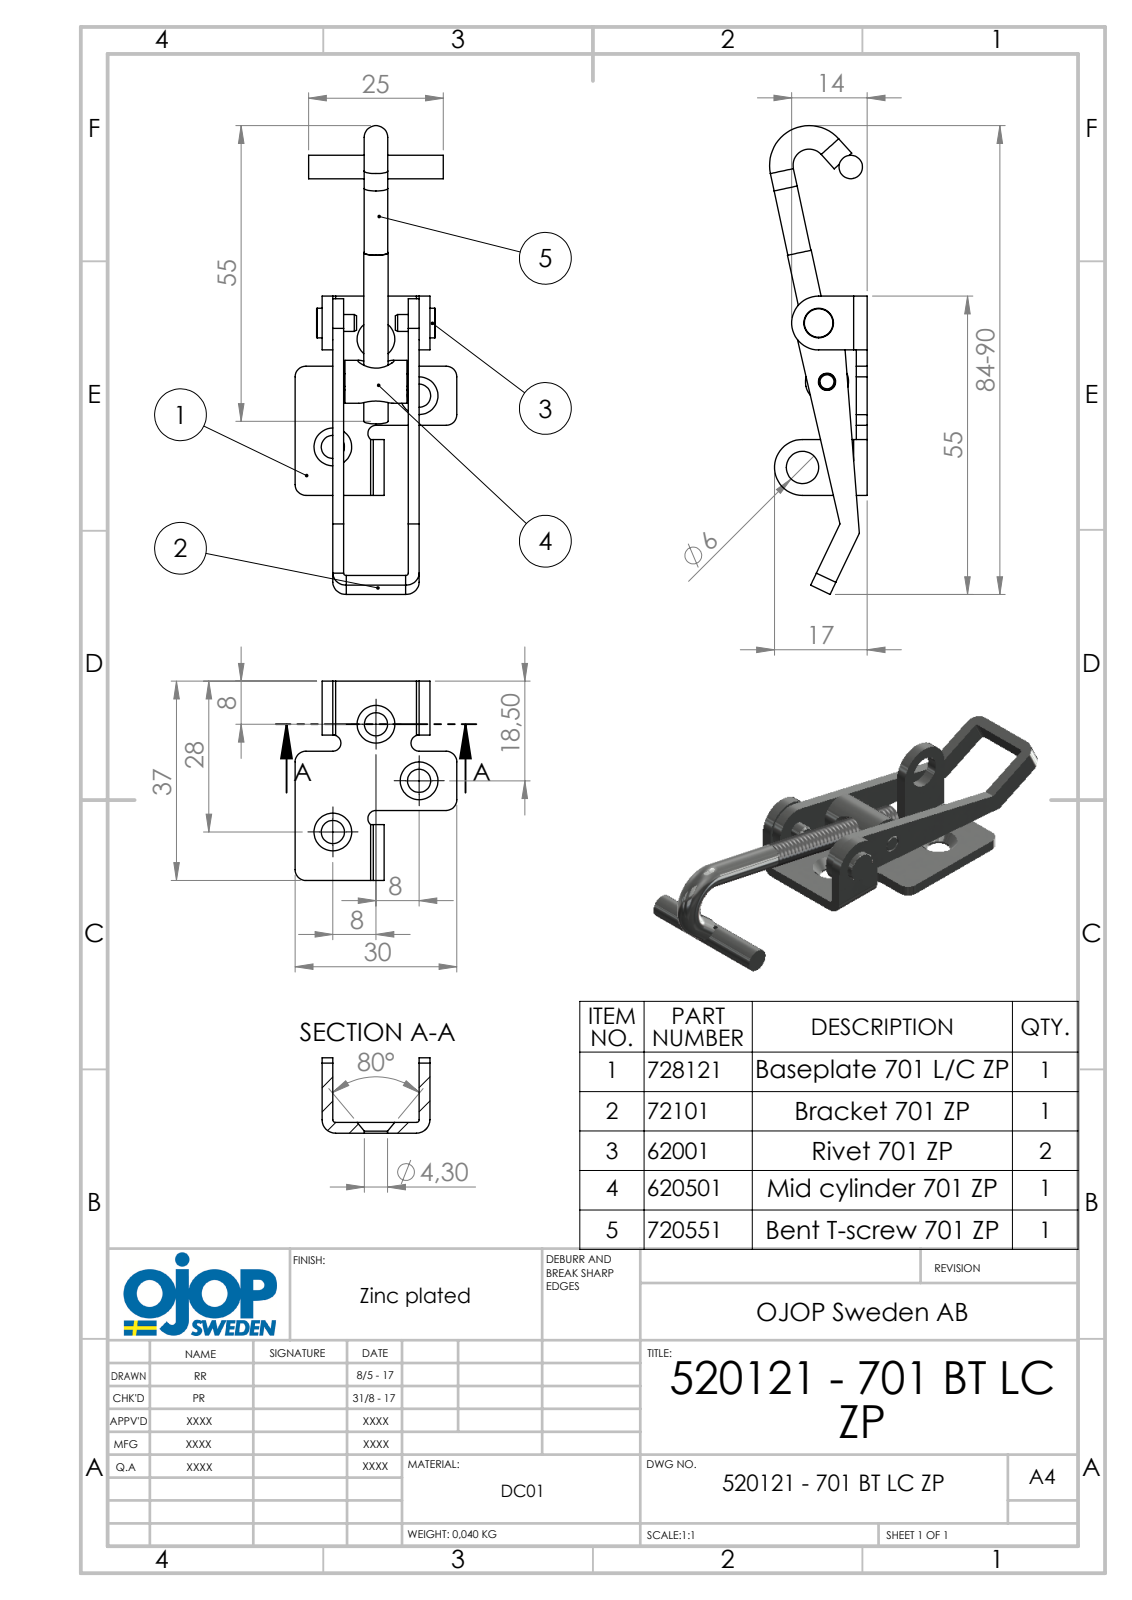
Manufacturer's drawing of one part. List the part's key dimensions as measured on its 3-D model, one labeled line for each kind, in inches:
Part name (STEP PRODUCT): 520121 - 701 TLC FZB; 701 - Mid Cylinder; Böjd T-skruv M5_Default<As Machined>; 701 - Ansatsnit (+2 more)
STEP written by: SolidWorks 2015 (AUTOMOTIVE_DESIGN)
Units: inches
Bodies: 6 solids, 164 faces (65 planar, 75 cylindrical, 24 other)
Overall size (bounding box): 3.606 × 1.181 × 0.758
Volume: 0.343 in³ · Surface area: 10.36 in²
Round holes (diameter × count): ⌀0.169 ×3, ⌀0.126 ×2, ⌀0.177 ×2, ⌀0.189 ×1
Round bosses / shafts (diameter × count): ⌀0.197 ×2, ⌀0.315 ×1, ⌀0.217 ×1, ⌀0.197 ×1, ⌀0.172 ×1, ⌀0.124 ×1, ⌀0.118 ×1
Partial cylindrical surfaces — rounded edges, fillets, slot ends (radius × count): R0.02 ×5, R0.098 ×5, R0.079 ×4, R0.059 ×3, R0.177 ×1, R0.197 ×1, R0.204 ×1
Main face-to-face distances: 0.079, 0.551, 0.63, 0.472, 0.157, 0.256, 0.295, 0.374, 0.335, 0.709
Hole centre spacings: 0.434, 0.52, 0.649, 0.733, 0.848, 1.061
